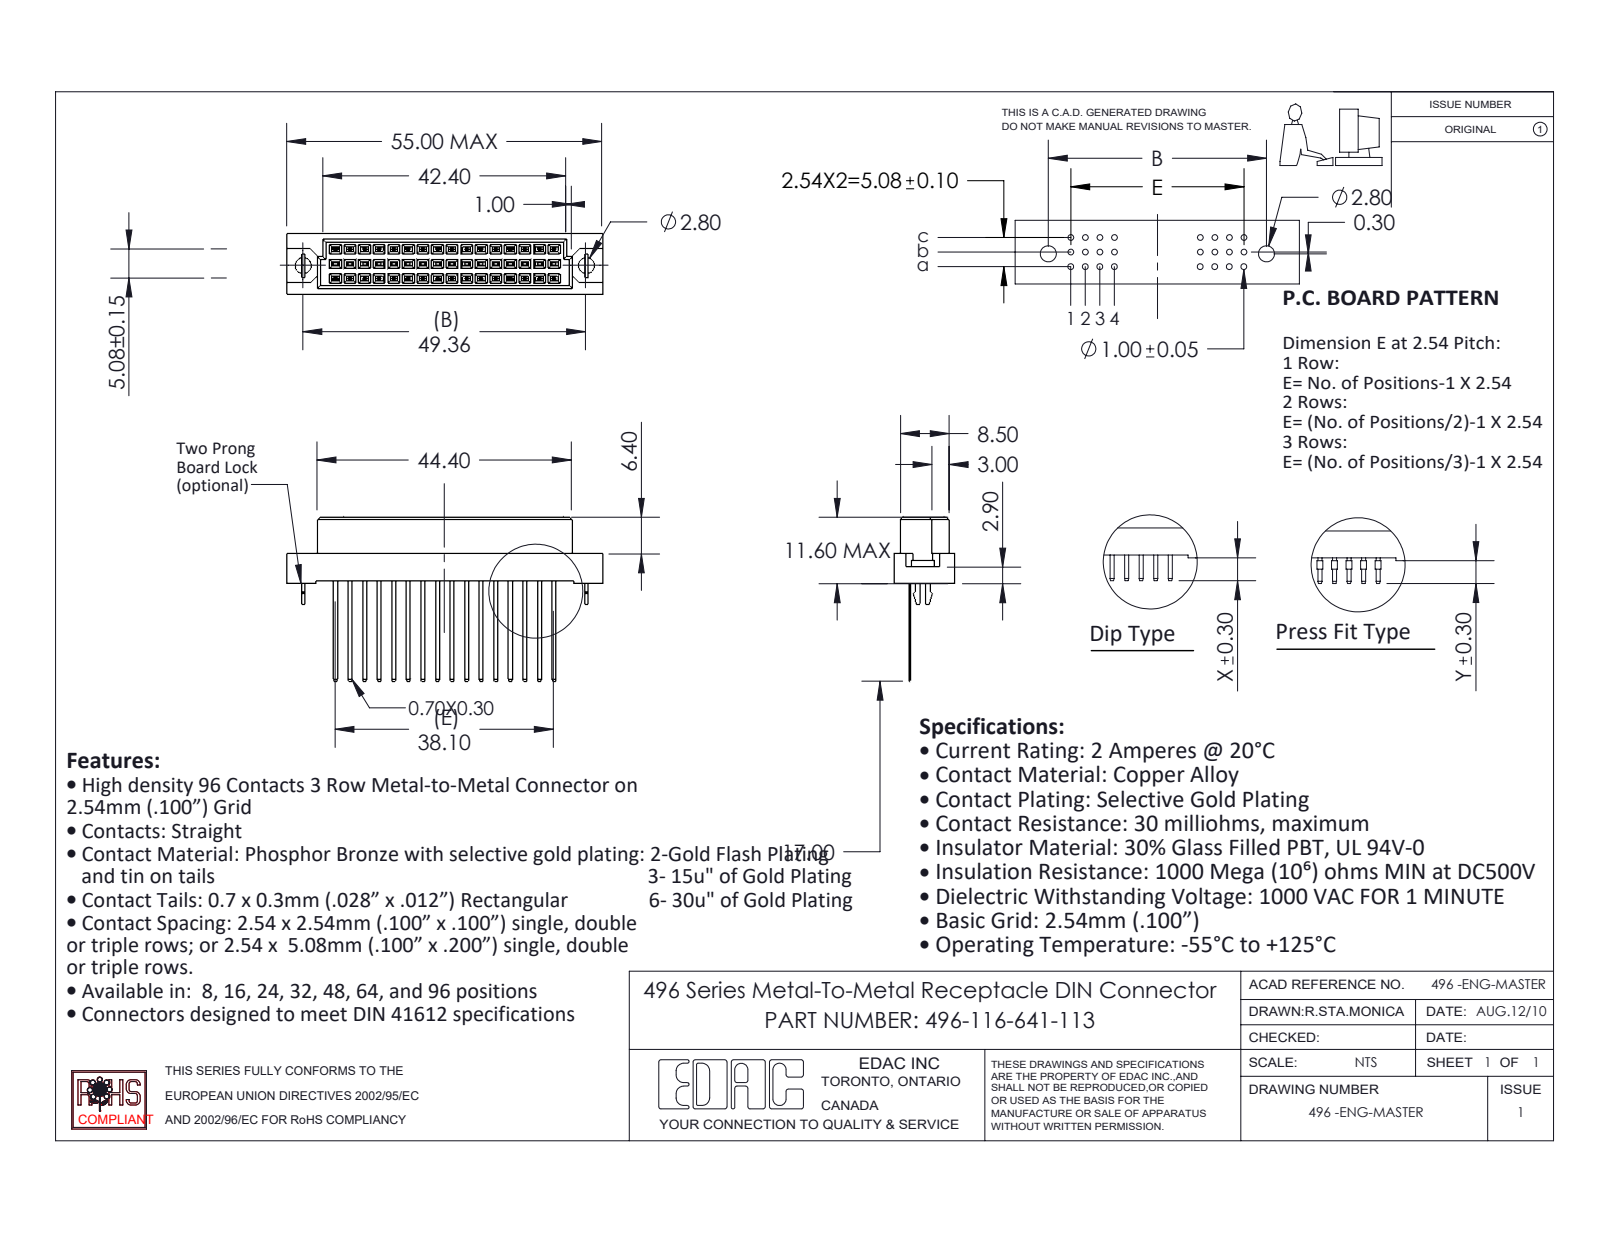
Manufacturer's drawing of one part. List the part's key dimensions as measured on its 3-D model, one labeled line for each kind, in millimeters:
Part name (STEP PRODUCT): 496-116-641-113; 496 Part_48; 496-290_41; 496 Bore-lock
STEP written by: SolidWorks 2020 (CONFIG_CONTROL_DESIGN)
Units: millimetres
Bodies: 19 solids, 862 faces (856 planar, 6 cylindrical, 0 other)
Overall size (bounding box): 55 × 28.6 × 10.6
Volume: 4 684 mm³ · Surface area: 5 017 mm²
Round holes (diameter × count): ⌀2.8 ×2
Partial cylindrical surfaces — rounded edges, fillets, slot ends (radius × count): R0.53 ×1
Main face-to-face distances: 2.54, 1.05, 9.55, 5.08, 0.81, 1.86, 1.56, 2.91, 7.69, 2.61
Hole centre spacings: 49.36
